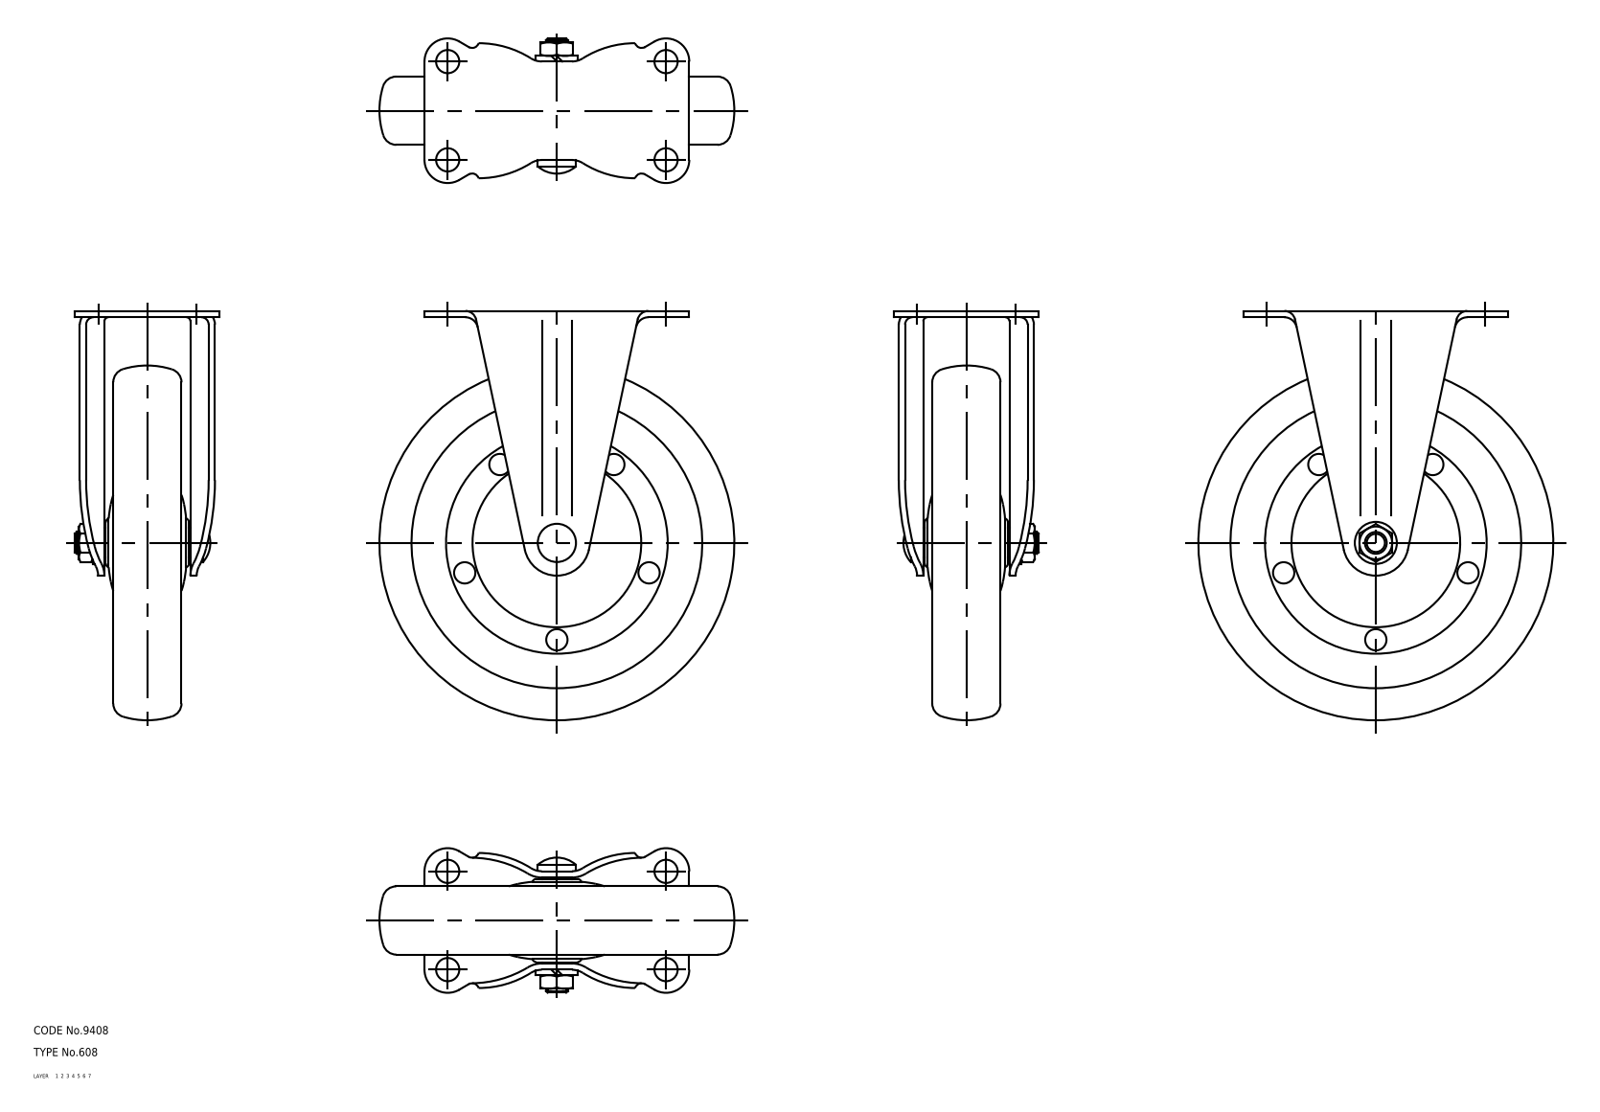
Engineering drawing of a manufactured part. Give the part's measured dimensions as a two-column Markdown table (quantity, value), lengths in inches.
| quantity | value |
| --- | --- |
| part name | wheel; axle; No_608_17663_36 |
| STEP written by | CADfix (AUTOMOTIVE_DESIGN) |
| units | inches |
| bodies | 3 solids, 178 faces (0 planar, 0 cylindrical, 178 other) |
| overall size | 5.906 × 5.118 × 2.087 |
| volume | 18.52 in³ |
| surface area | 98.35 in² |
